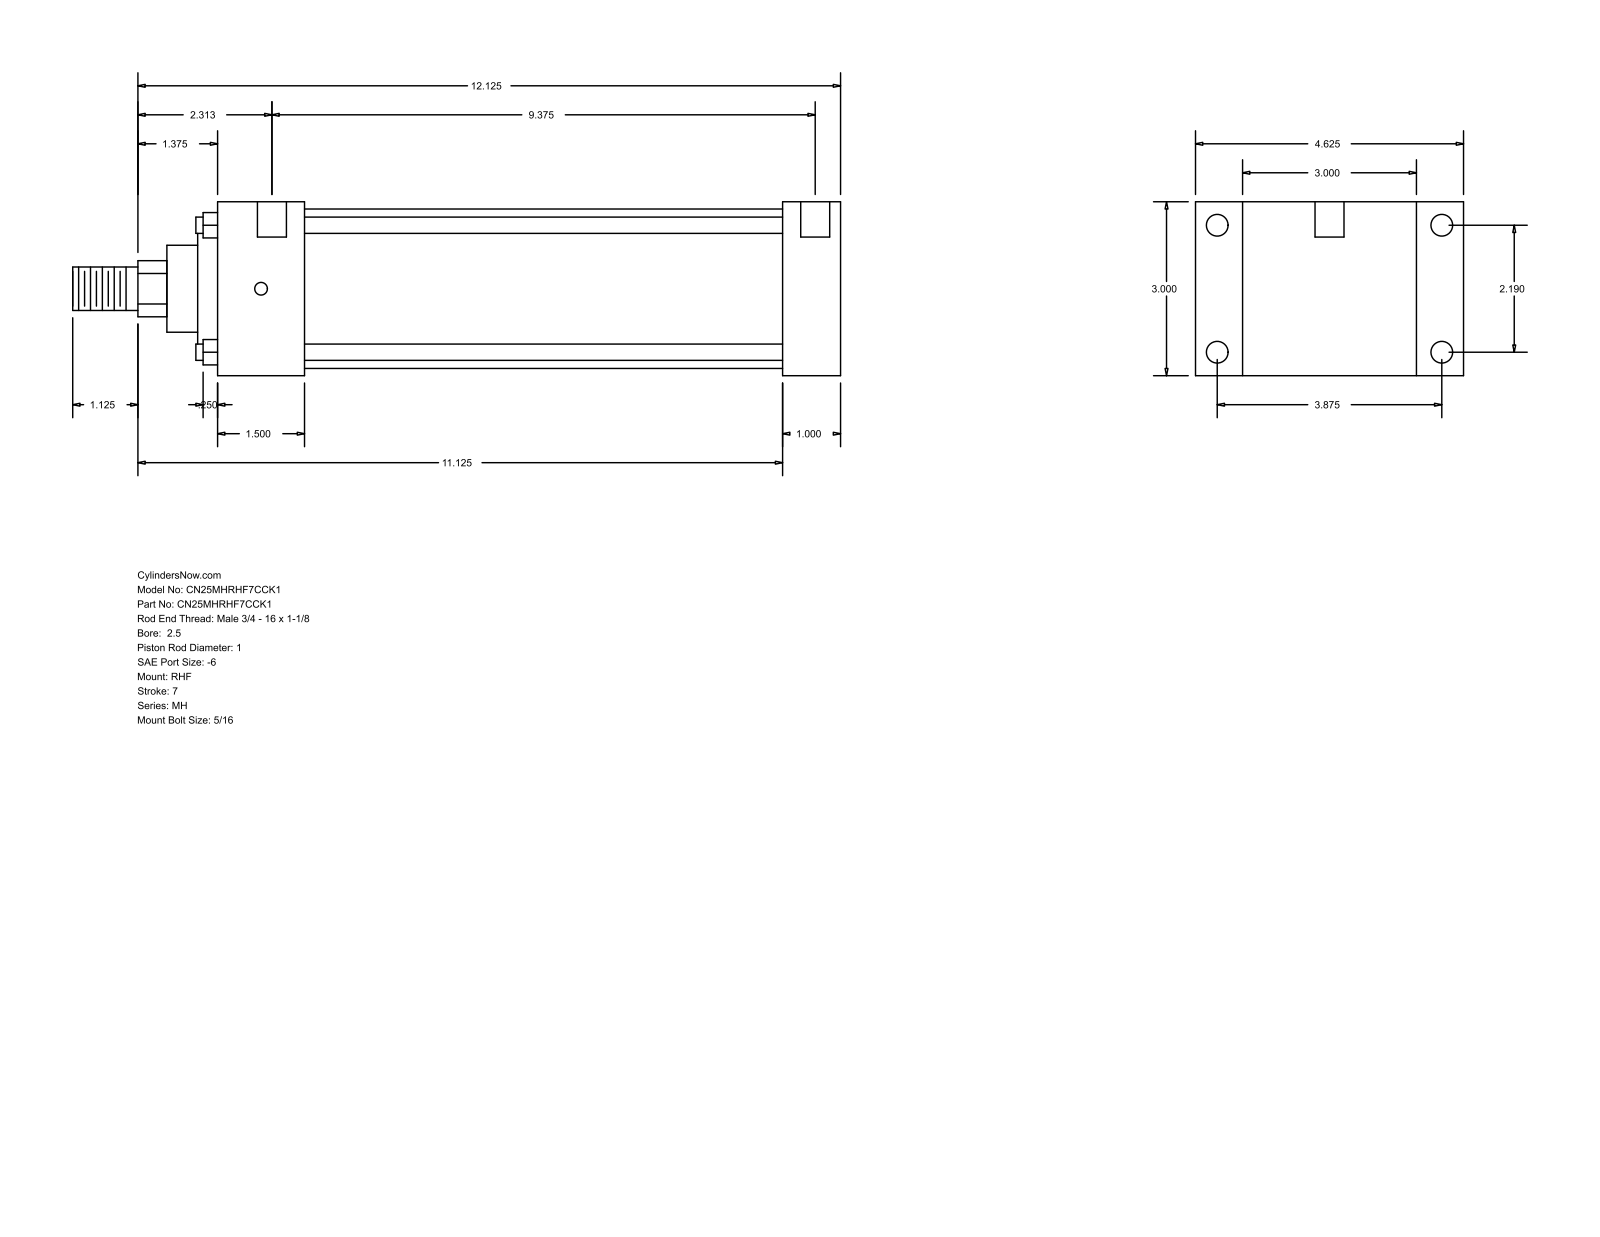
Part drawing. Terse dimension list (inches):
name: MH_RHF__0250_1
written by: GSSL Pune (CONFIG_CONTROL_DESIGN)
unit: in
bodies: 0 solids, 90 faces (61 planar, 29 cylindrical, 0 other)
size: 13.25 × 4.625 × 3
holes: 4× ⌀0.219, 4× ⌀0.375, 2× ⌀0.5
bosses: 4× ⌀0.281, 1× ⌀2.75, 1× ⌀2.375, 1× ⌀1.5, 1× ⌀1, 1× ⌀0.75
rounds: 1× R0.484
face distances: 3, 1, 0.813, 3.813, 9.75, 10.75, 4.625, 1.5, 8.25, 9.25
hole spacings: 2.19, 3.875, 4.451, 9.687, 0.125, 0.187, 9.375, 9.5
